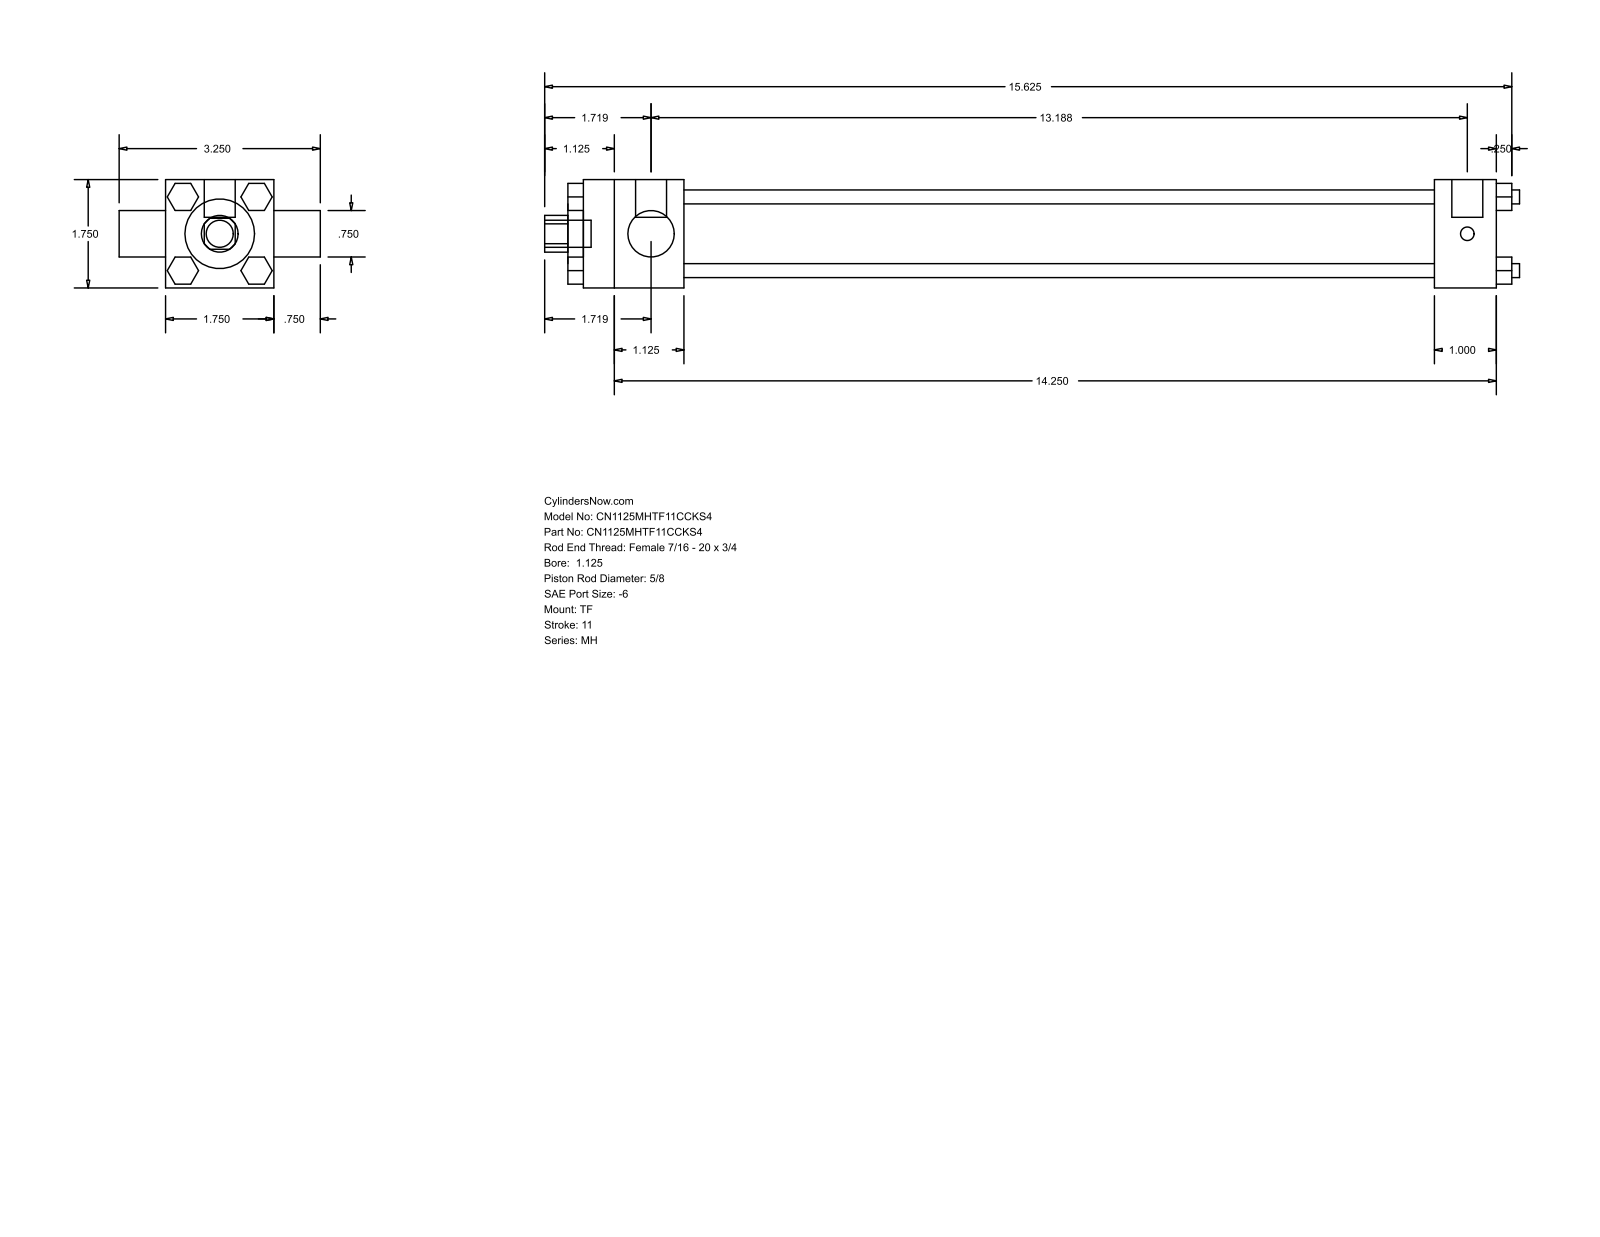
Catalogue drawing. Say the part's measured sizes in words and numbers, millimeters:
The part is named "MH_TF__0112_0.625". Its 3-D file was written by "GSSL Pune (CONFIG_CONTROL_DESIGN)". It is 0 solids with 120 faces: 92 planar, 28 cylindrical and 0 other. Overall it measures 400.05 by 82.55 by 44.45 millimeters. Round holes: 1 of diameter 15.88, 1 of diameter 19.05, 1 of diameter 28.57, 1 of diameter 34.92. Round bosses or shafts: 4 of diameter 5.71, 3 of diameter 5.56, 2 of diameter 12.7, 1 of diameter 11.11. Partial cylindrical surfaces (rounded edges, fillets, slot ends): 1 of radius 7.54. The main face-to-face distances are 44.46, 11.11, 307.97, 333.37, 25.4, 41.27, 349.24, 374.64, 47.62, 6.35.
